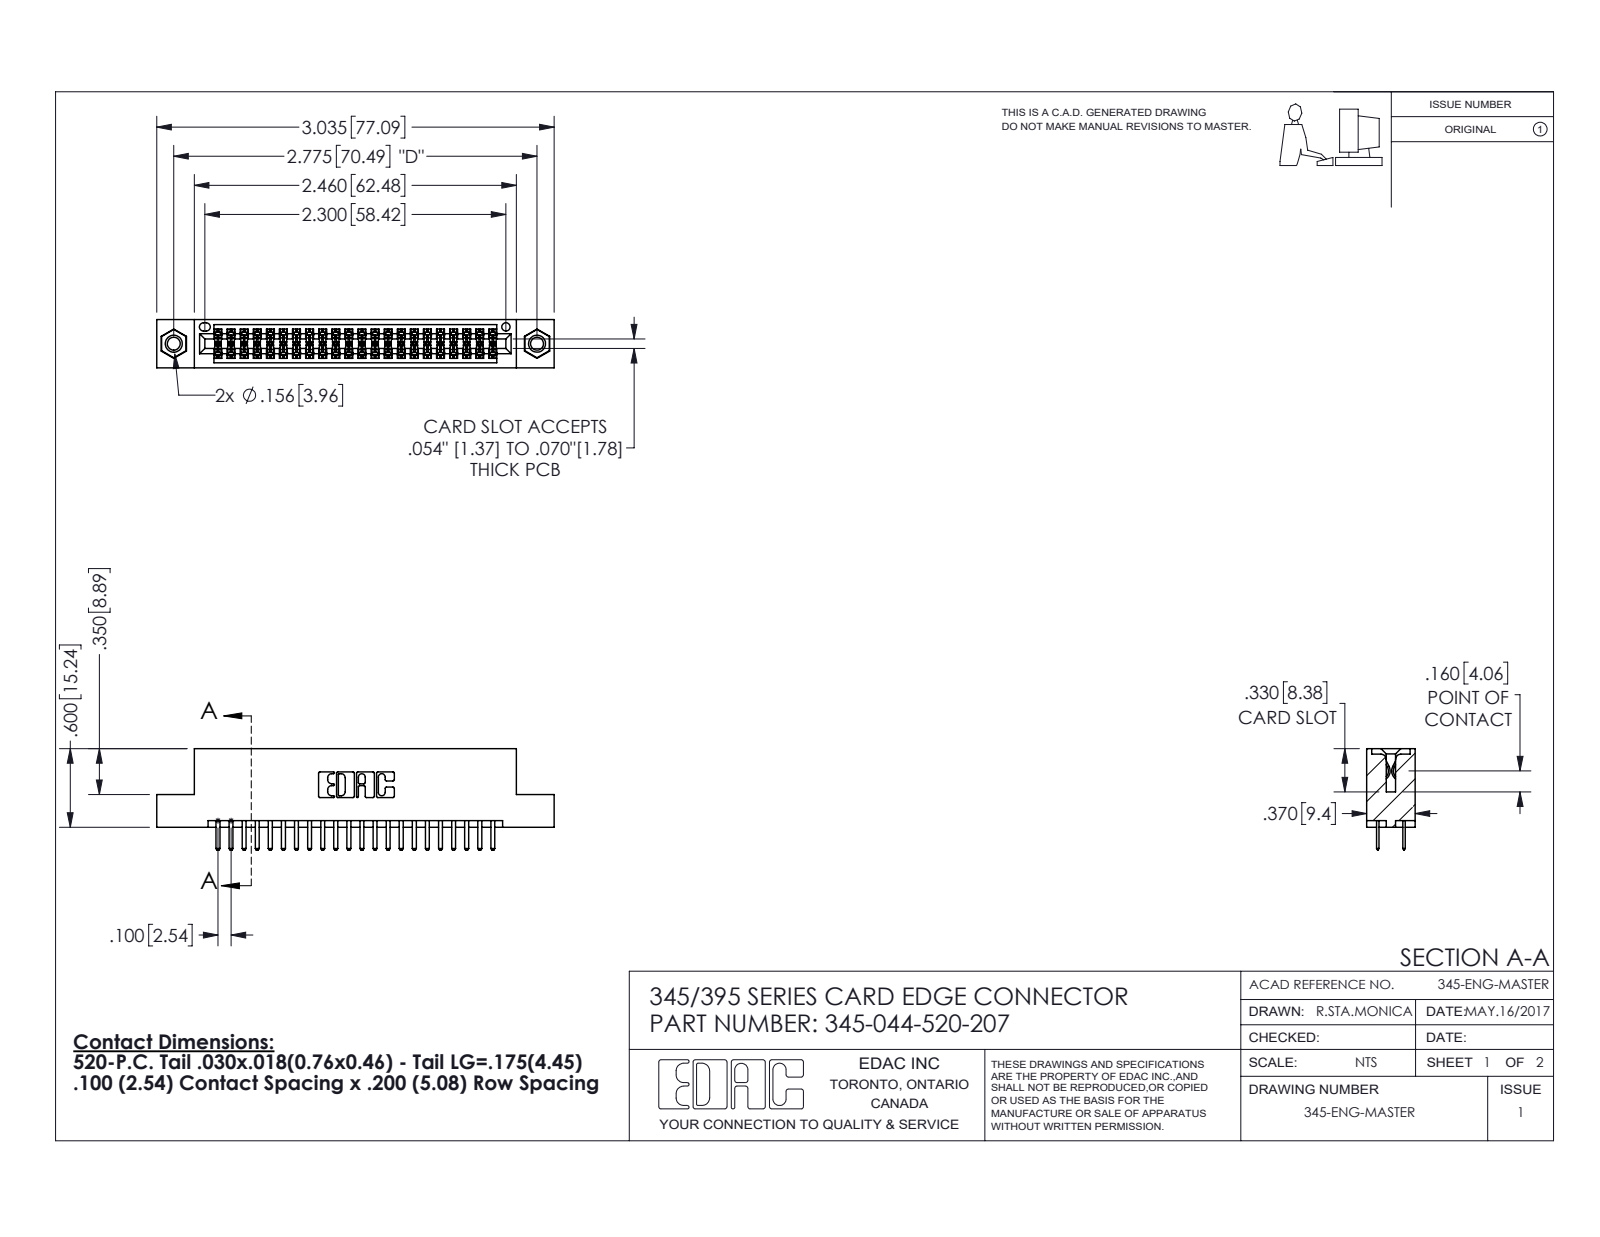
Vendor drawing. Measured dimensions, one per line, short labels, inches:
name: 345 Part_Flush Mounting Lugs - 0.156 Dia-TI; 345-044-520-207; 345-250-001_345-250-005-103; 345-292-001_345-293-120
written by: SolidWorks 2016 (CONFIG_CONTROL_DESIGN)
unit: in
bodies: 47 solids, 2562 faces (1652 planar, 894 cylindrical, 16 other)
size: 3.035 × 0.775 × 0.37
volume: 0.444 in³; area: 16.04 in²
holes: 2× ⌀0.098, 2× ⌀0.125, 2× ⌀0.156, 1× ⌀0.064
bosses: 2× ⌀0.155
rounds: 66× R0.006, 48× R0.01, 22× R0.01, 6× R0.007, 6× R0.031, 3× R0.026, 2× R0.014, 2× R0.019
face distances: 0.072, 0.298, 0.2, 0.37, 0.098, 0.272, 0.025, 0.225, 0.022, 0.072
hole spacings: 0.27, 2.541, 2.775
